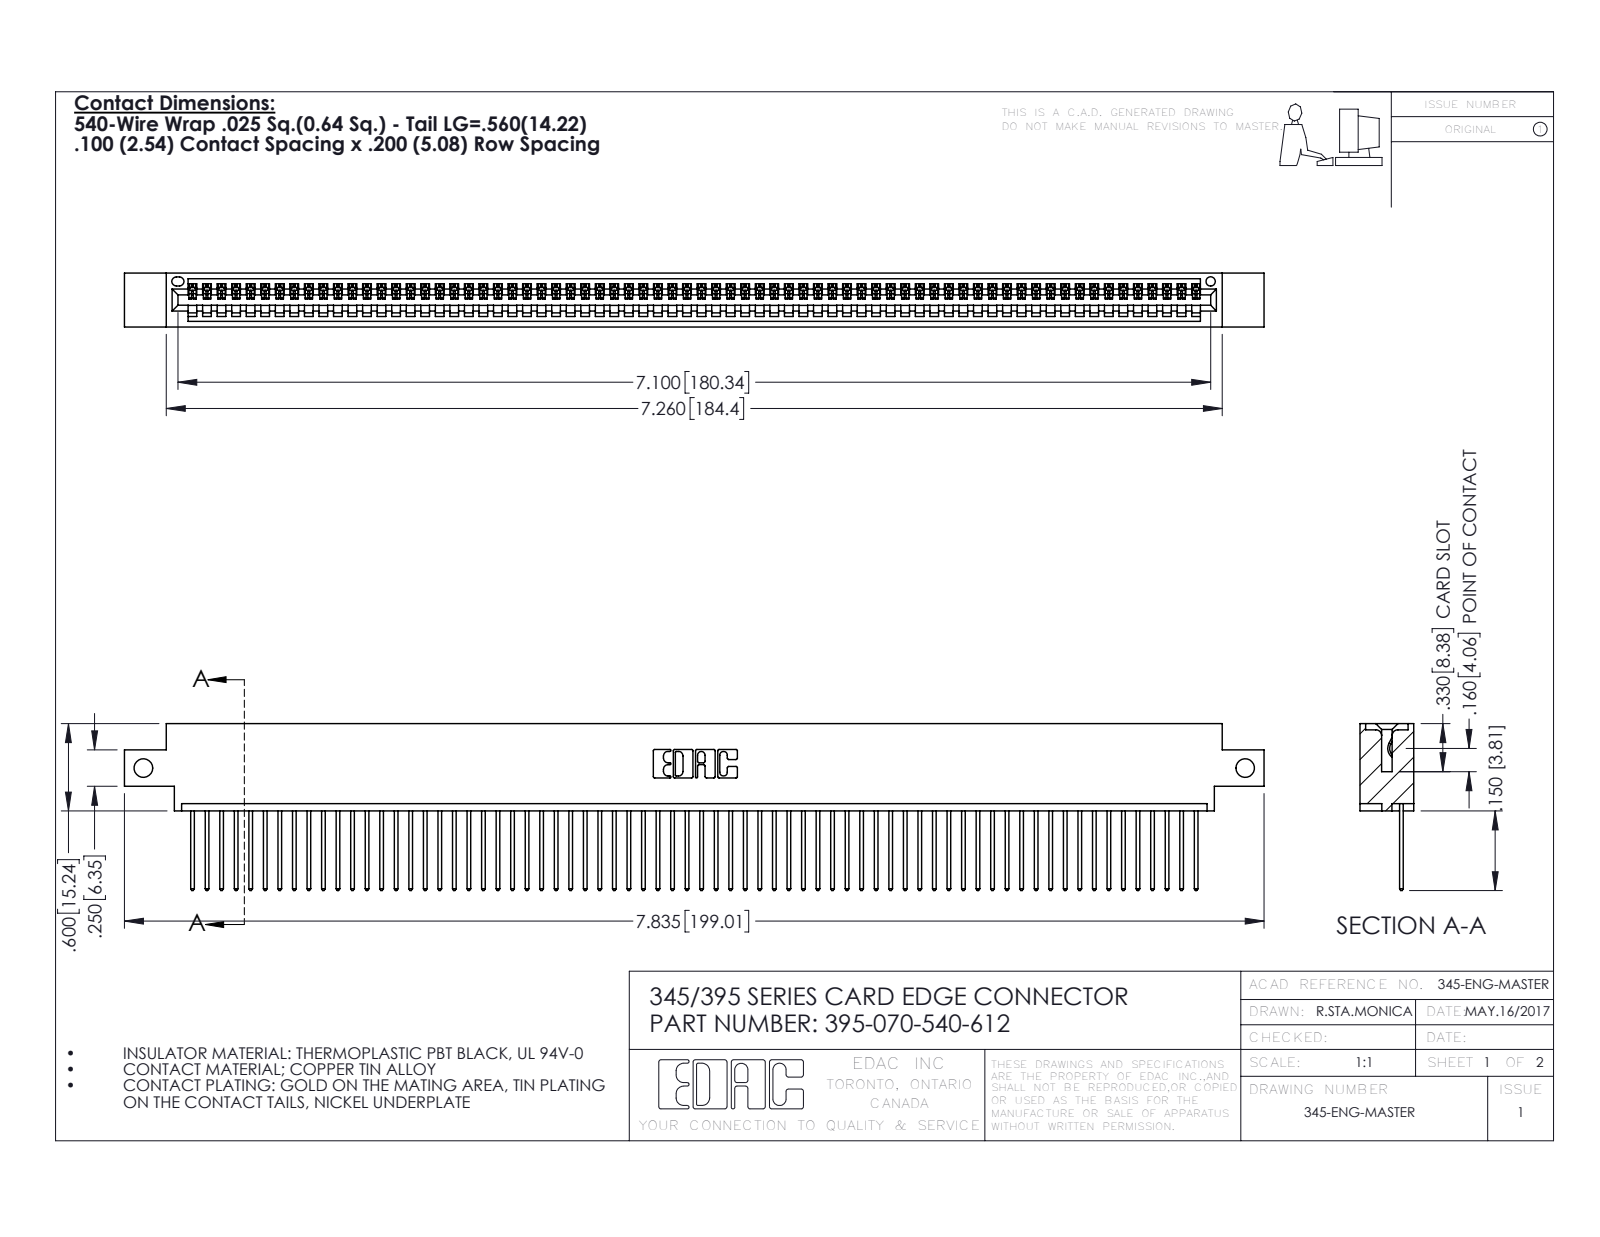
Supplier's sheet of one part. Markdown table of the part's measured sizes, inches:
| quantity | value |
| --- | --- |
| part name | 395-070-540-612; 345-292-001_345-293-140; 345 Part_0.170 Offset - Side Mount |
| STEP written by | SolidWorks 2016 (CONFIG_CONTROL_DESIGN) |
| units | inches |
| bodies | 71 solids, 4190 faces (2884 planar, 1306 cylindrical, 0 other) |
| overall size | 7.835 × 1.147 × 0.37 |
| volume | 1.161 in³ |
| surface area | 40.81 in² |
| round holes (diameter × count) | 0.128 × 2, 0.064 × 1 |
| partial cylindrical surfaces (radius × count) | 0.006 × 140, 0.01 × 140, 0.01 × 22, 0.007 × 6, 0.031 × 6, 0.026 × 3, 0.031 × 2, 0.04 × 2 |
| main face-to-face distances | 0.072, 0.298, 0.37, 0.098, 0.272, 0.025, 0.2, 0.225, 0.175, 0.149 |
| hole center spacings | 7.575 |
